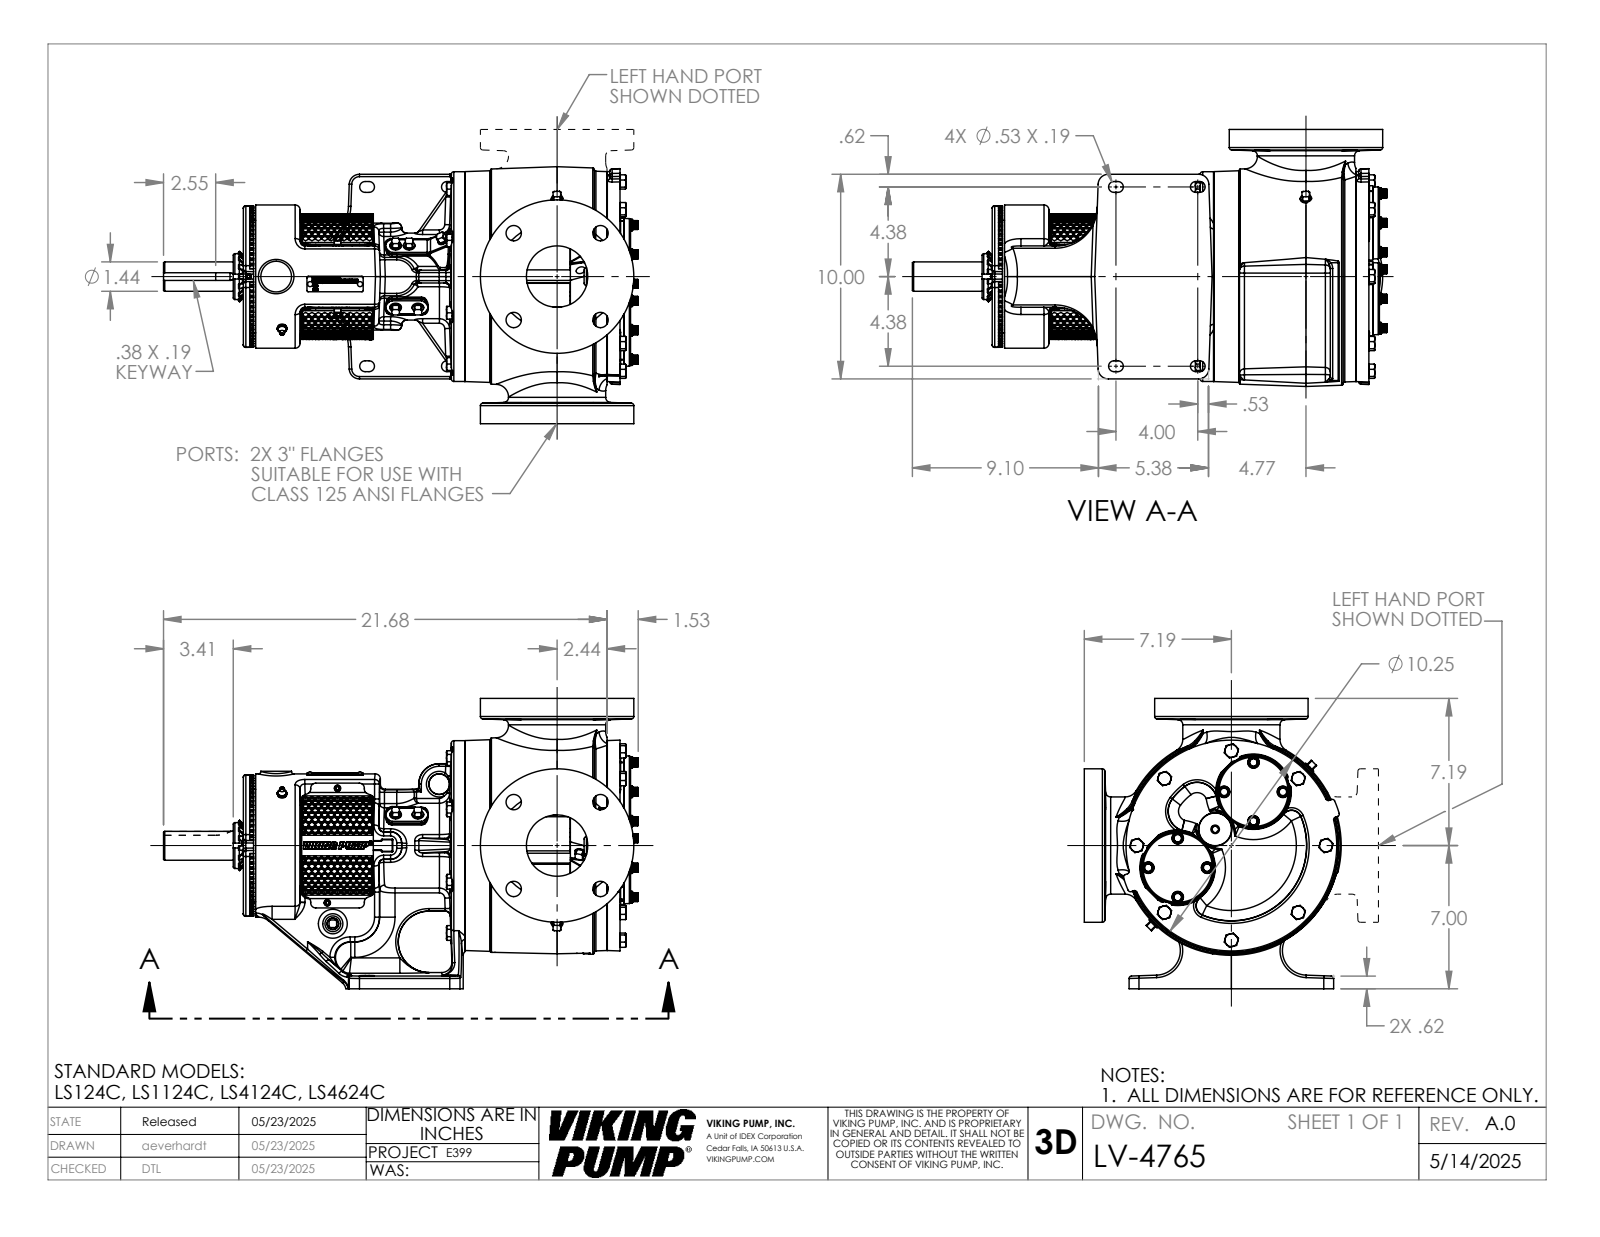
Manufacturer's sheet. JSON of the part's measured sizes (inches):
{"part_name": "LV-4765", "step_written_by": "SolidWorks 2024 (AUTOMOTIVE_DESIGN)", "units": "inches", "bodies": {"solids": 1, "faces": 4489, "planar": 1546, "cylindrical": 932, "other": 2011}, "overall_size": [23.206, 14.19, 12.56], "volume_in3": 1053, "surface_area_in2": 1399, "round_holes": [[0.75, 8], [1.094, 8], [0.199, 6], [0.25, 6], [0.159, 3], [0.266, 2], [0.313, 2], [1.506, 1], [1.577, 1], [1.593, 1], [1.83, 1], [2.44, 1]], "round_bosses_or_shafts": [[0.625, 15], [0.563, 8], [0.437, 3], [0.312, 3], [7.5, 2], [4.75, 2], [3.5, 2], [10.25, 1]], "partial_cylinders_radius": [[0.063, 109], [0.069, 74], [0.12, 74], [0.24, 48], [0.03, 20], [0.5, 14], [0.25, 12], [0.75, 12]], "face_to_face_distances": [14.19, 1.5, 15.664, 3.534, 12.13, 0.5, 16.179, 12.645, 0.515, 2.25], "hole_center_spacings": [3, 4.243, 1.375, 2.18, 3.609, 4.446, 4.625, 6.404]}
